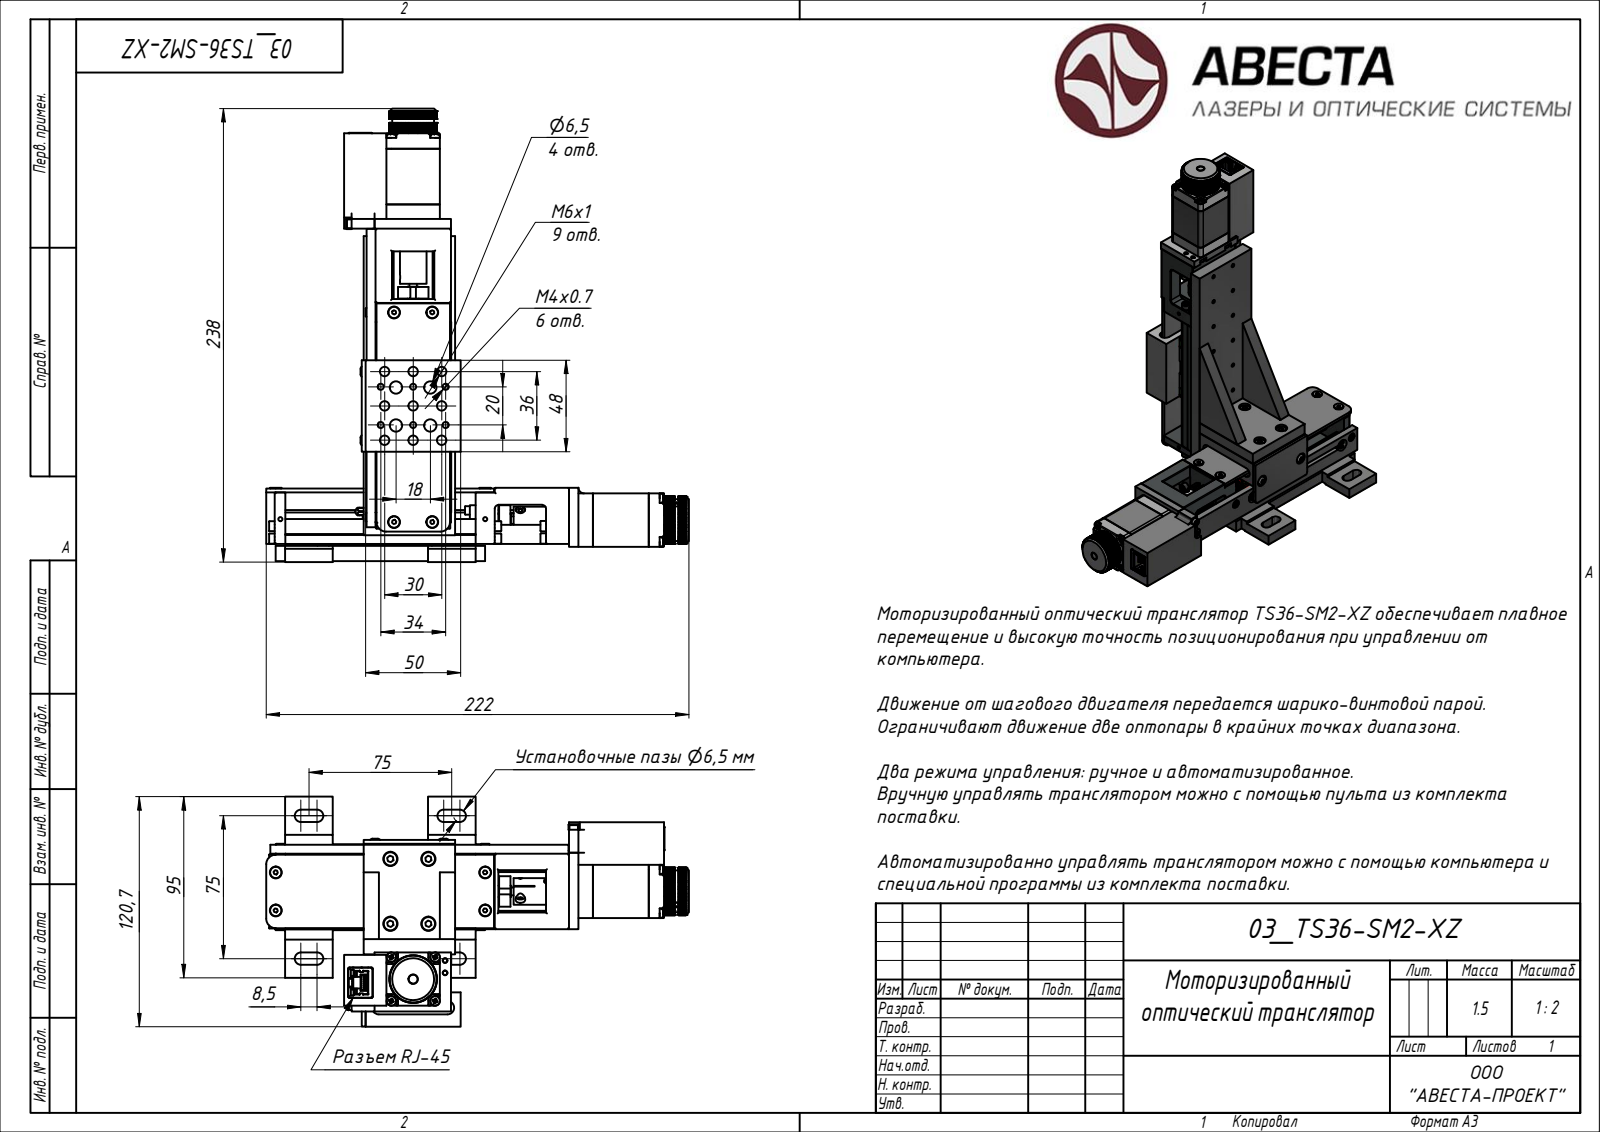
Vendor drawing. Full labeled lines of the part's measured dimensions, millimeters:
STEP written by: Rhino 7.34 (AUTOMOTIVE_DESIGN)
Units: millimetres
Bodies: 1 solid, 4764 faces (2894 planar, 1298 cylindrical, 572 other)
Overall size (bounding box): 238 × 222 × 120.7
Volume: 536 469 mm³ · Surface area: 213 498 mm²
Round holes (diameter × count): ⌀3.4 ×16, ⌀6.5 ×16, ⌀2.46 ×15, ⌀3.24 ×15, ⌀7.5 ×15, ⌀4.92 ×14, ⌀1.05 ×10, ⌀2.5 ×10, ⌀3.8 ×8, ⌀5 ×8, ⌀2.15 ×6, ⌀2.46 ×6
Round bosses / shafts (diameter × count): ⌀4.5 ×20, ⌀3 ×12, ⌀6 ×10, ⌀5.5 ×10, ⌀5.3 ×8, ⌀7 ×6, ⌀5 ×6, ⌀2.5 ×6
Partial cylindrical surfaces — rounded edges, fillets, slot ends (radius × count): R0.5 ×72, R2.5 ×20, R3 ×20, R2 ×16, R1 ×8, R3.25 ×8, R1.23 ×7, R1.23 ×7
Main face-to-face distances: 8, 0.5, 2.5, 2, 7, 29.5, 4.5, 28, 3, 27.5
Hole centre spacings: 20, 18, 26.91, 60, 62.64, 40, 1, 10
